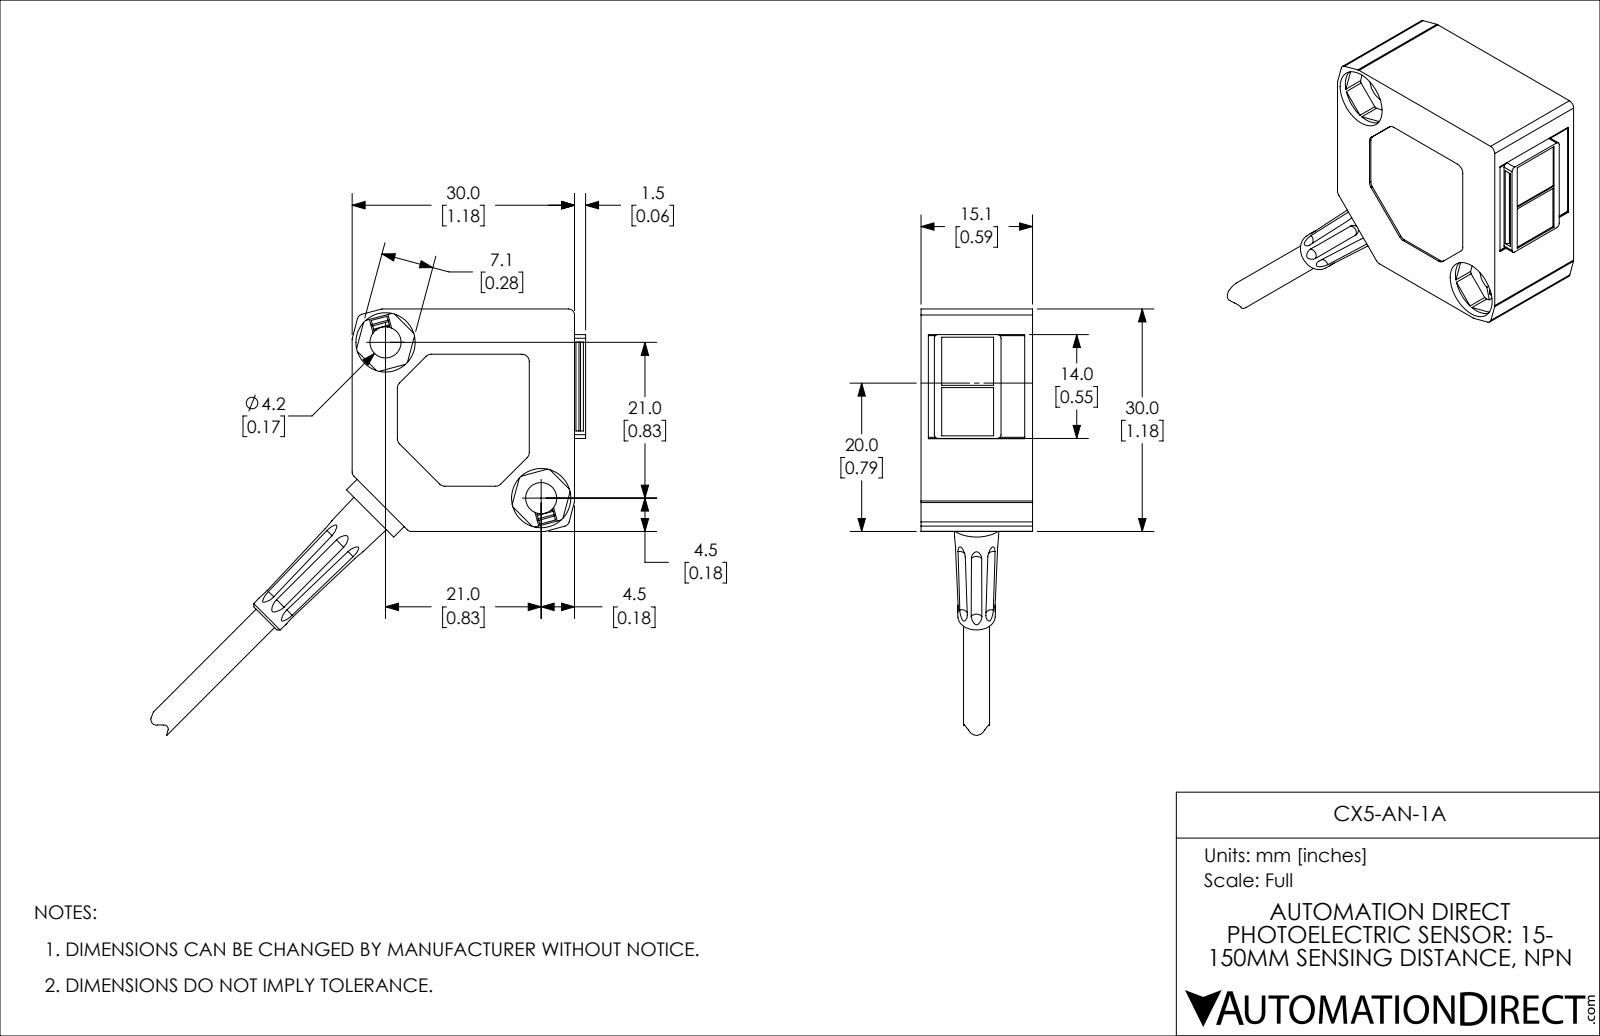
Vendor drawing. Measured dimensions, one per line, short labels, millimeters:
name: LHK_3031_301
written by: SolidWorks 2021 (AUTOMOTIVE_DESIGN)
unit: mm
bodies: 1 solid, 198 faces (116 planar, 62 cylindrical, 20 other)
size: 62.07 × 57.5 × 14.85
volume: 13 174 mm³; area: 4 946 mm²
holes: 2× ⌀2.2, 2× ⌀4.2, 2× ⌀8, 1× ⌀1.85, 1× ⌀7.6
bosses: 1× ⌀3.5
rounds: 17× R0.8, 7× R1, 4× R0.2, 2× R0.15, 2× R0.3, 2× R0.46, 2× R4.5, 1× R0.56
face distances: 14.85, 30, 14.6, 3.8, 11.05, 7.1, 3.55, 0.92, 33.75, 4.9
hole spacings: 1.73, 4.4, 5, 5.47, 5.86, 5.96, 29.7
